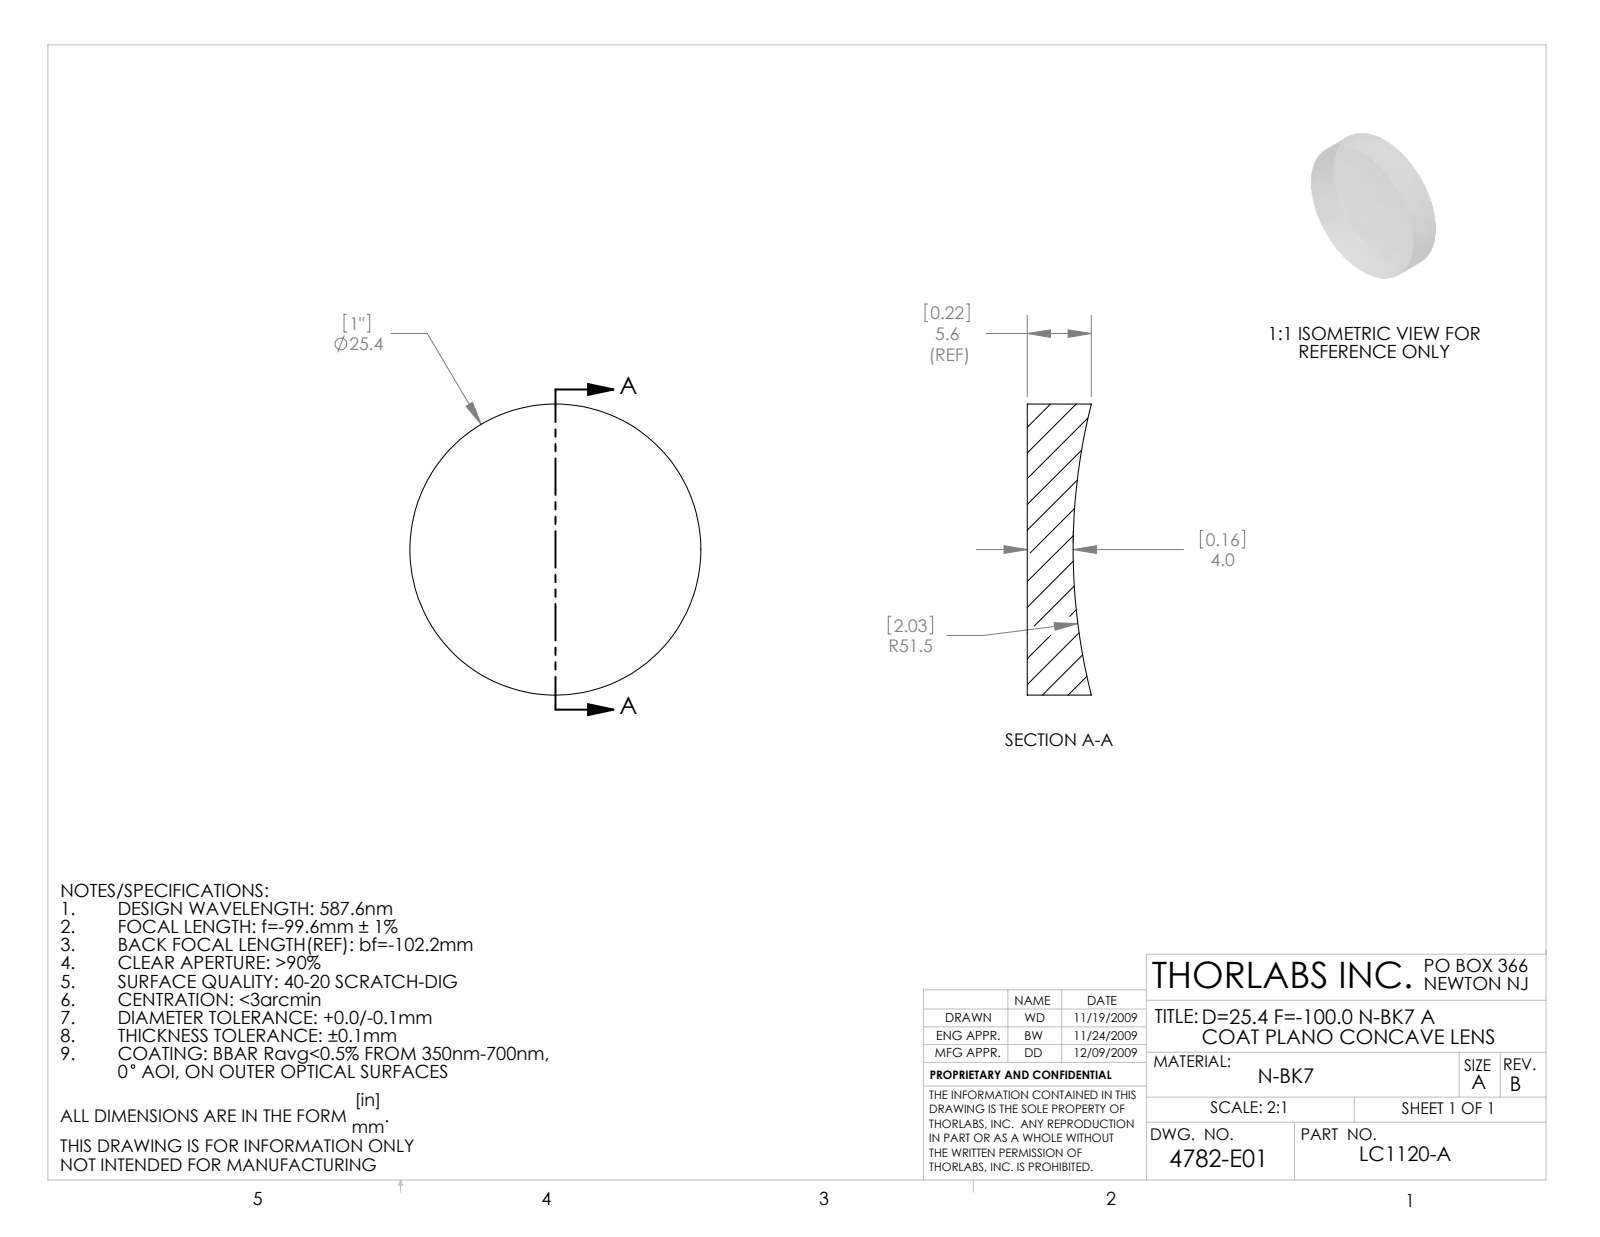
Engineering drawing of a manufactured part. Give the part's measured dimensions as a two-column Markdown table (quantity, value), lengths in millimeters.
| quantity | value |
| --- | --- |
| part name | 4782-E0W |
| STEP written by | SolidWorks 2009 (AUTOMOTIVE_DESIGN) |
| units | millimeters |
| bodies | 1 solid, 5 faces (1 planar, 2 cylindrical, 2 other) |
| overall size | 25.4 × 25.4 × 5.59 |
| volume | 2 428 mm³ |
| surface area | 1 468 mm² |
| round bosses / shafts (diameter × count) | 25.4 × 1 |
